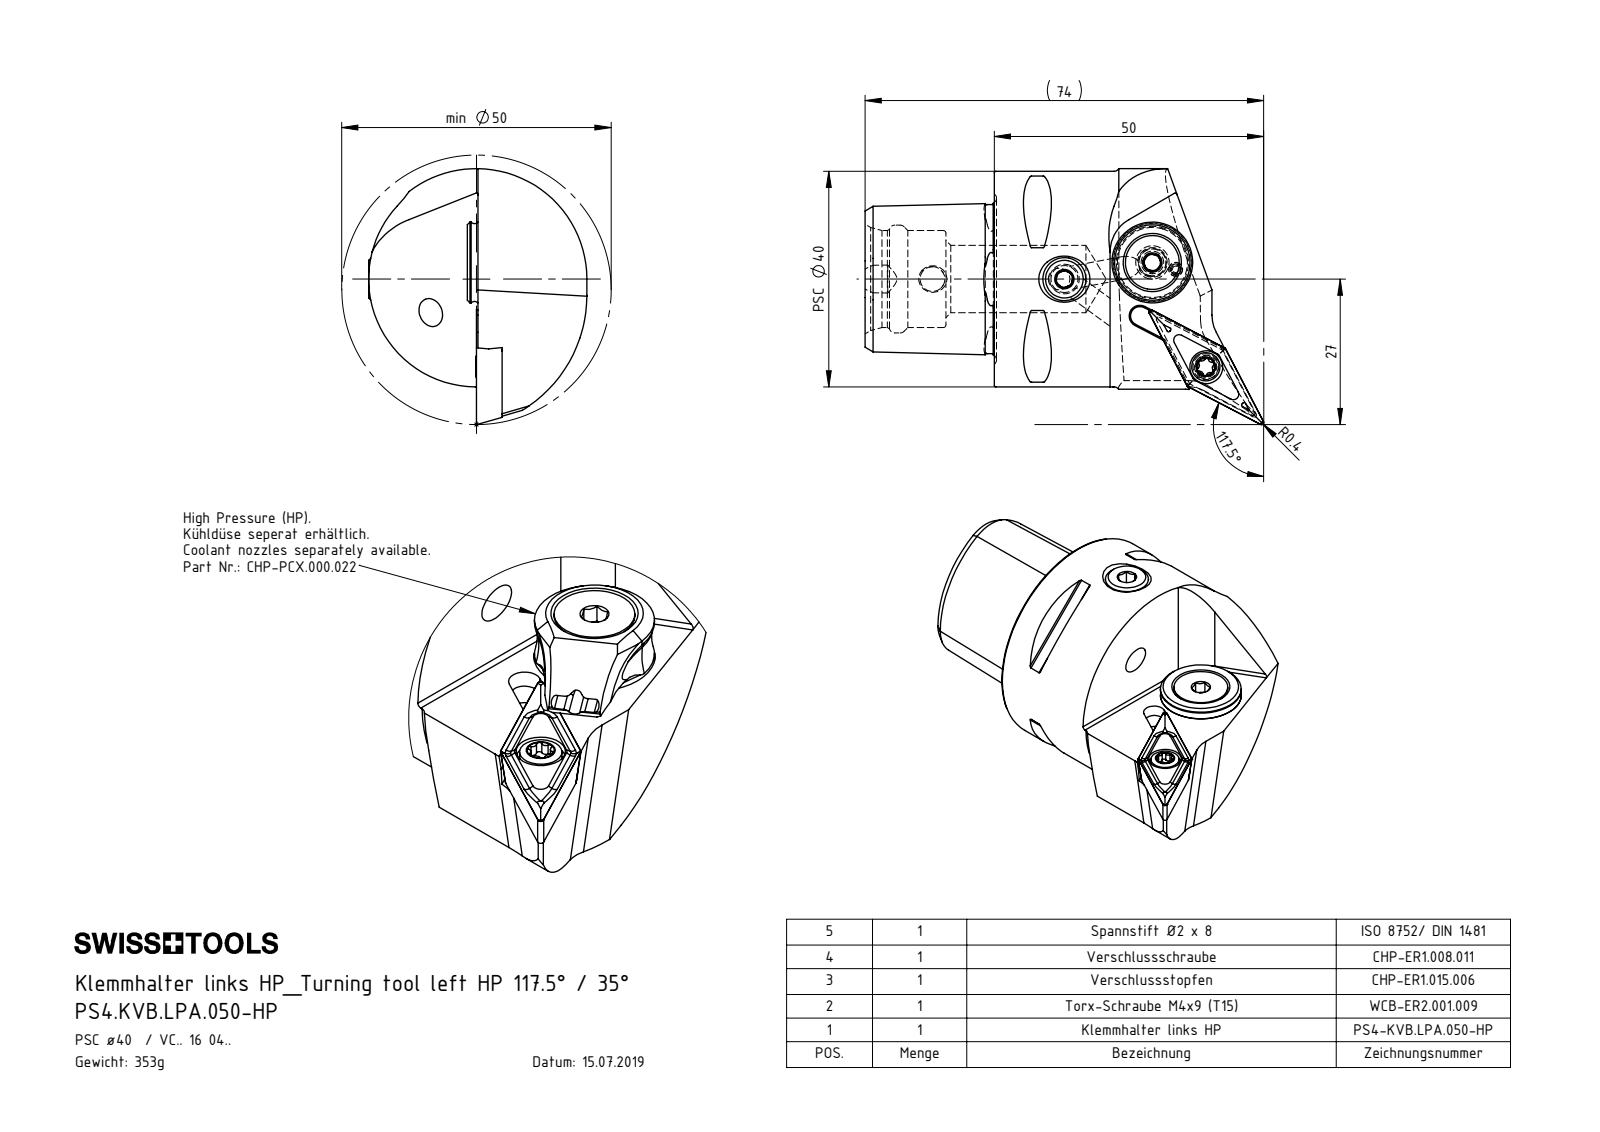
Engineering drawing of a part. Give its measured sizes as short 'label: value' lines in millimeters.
name: CHP-ER1.015.006; DIN 7991 - M5x15; VCMT160404; DIN 3771 - 13x1 (+6 more)
written by: SolidWorks 2017 (AUTOMOTIVE_DESIGN)
unit: mm
bodies: 8 solids, 393 faces (94 planar, 101 cylindrical, 198 other)
size: 74 × 47.5 × 40.5
volume: 44 827 mm³; area: 15 073 mm²
holes: 3× ⌀4.2, 1× ⌀1.2, 1× ⌀2, 1× ⌀2.5, 1× ⌀3, 1× ⌀3.3, 1× ⌀4, 1× ⌀4.4, 1× ⌀4.6, 1× ⌀5, 1× ⌀5.2, 1× ⌀6.1
bosses: 1× ⌀40, 1× ⌀15, 1× ⌀13.4, 1× ⌀10, 1× ⌀8, 1× ⌀5.5, 1× ⌀5.25, 1× ⌀5
rounds: 8× R0.3, 6× R0.34, 6× R0.59, 3× R7, 2× R0.5, 1× R1.75, 1× R3, 1× R20.5
face distances: 21.5, 4.5, 4.46, 24, 45.5, 15.52, 15, 35.3, 9, 6.4
hole spacings: 1, 4.5, 16.62, 17.6, 18.91, 19.01, 20.72, 21.71
